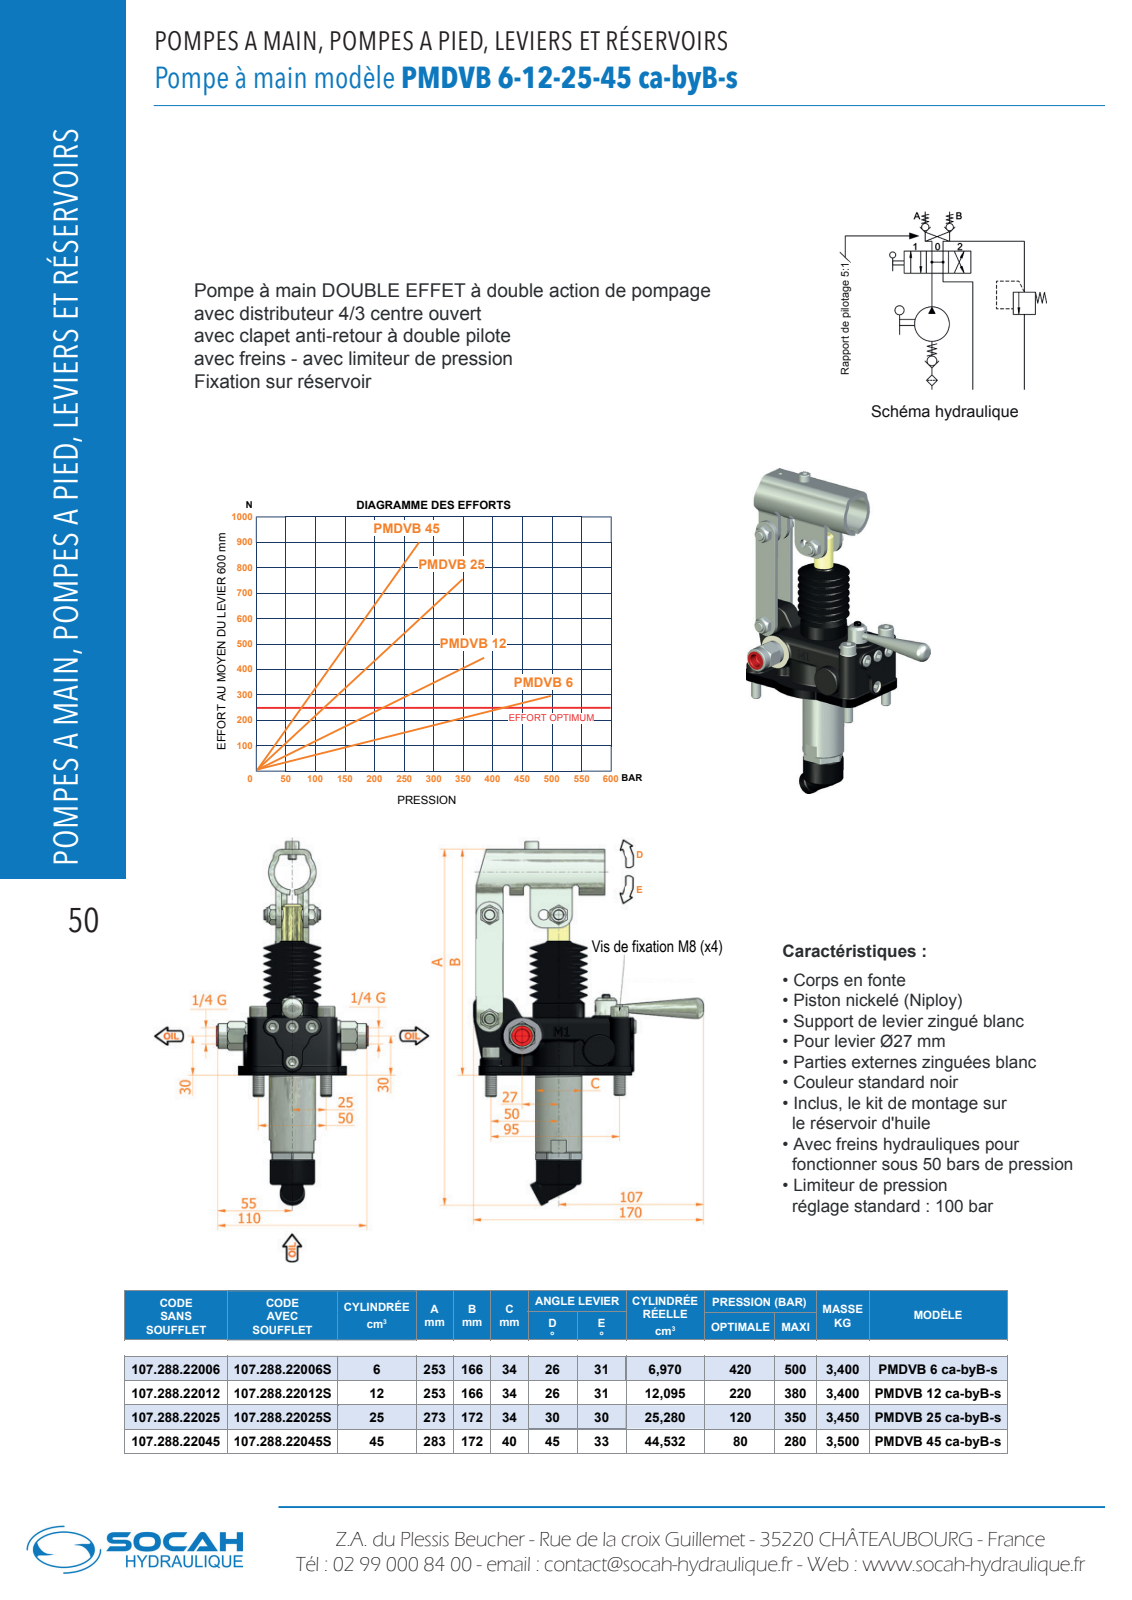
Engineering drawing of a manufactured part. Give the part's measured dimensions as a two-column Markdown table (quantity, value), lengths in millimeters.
| quantity | value |
| --- | --- |
| part name | 6061.0101.00.50 Derivazione 2 |
| STEP written by | Autodesk Inventor 2013 (AUTOMOTIVE_DESIGN) |
| units | millimeters |
| bodies | 18 solids, 1655 faces (764 planar, 364 cylindrical, 527 other) |
| overall size | 277.85 × 170 × 112 |
| volume | 10 417 mm³ |
| surface area | 150 688 mm² |
| round holes (diameter × count) | 4.92 × 6, 8 × 6, 1.2 × 4, 4 × 4, 14 × 4, 10 × 3, 10.92 × 2, 13 × 2, 3 × 1, 5 × 1, 6.5 × 1, 10.5 × 1 |
| round bosses / shafts (diameter × count) | 10 × 5, 8 × 5, 13 × 4, 12 × 4, 8.5 × 4, 11.05 × 3, 6 × 3, 18 × 2 |
| partial cylindrical surfaces (radius × count) | 1 × 30, 0.2 × 24, 0.1 × 16, 5 × 15, 2 × 14, 3 × 9, 8 × 9, 1.2 × 8 |
| main face-to-face distances | 4, 20, 42, 5, 2, 37, 16, 44, 7, 26 |
| hole center spacings | 14.5, 3.6, 29, 12.5, 19.14, 24.83, 25.5, 26.77 |
